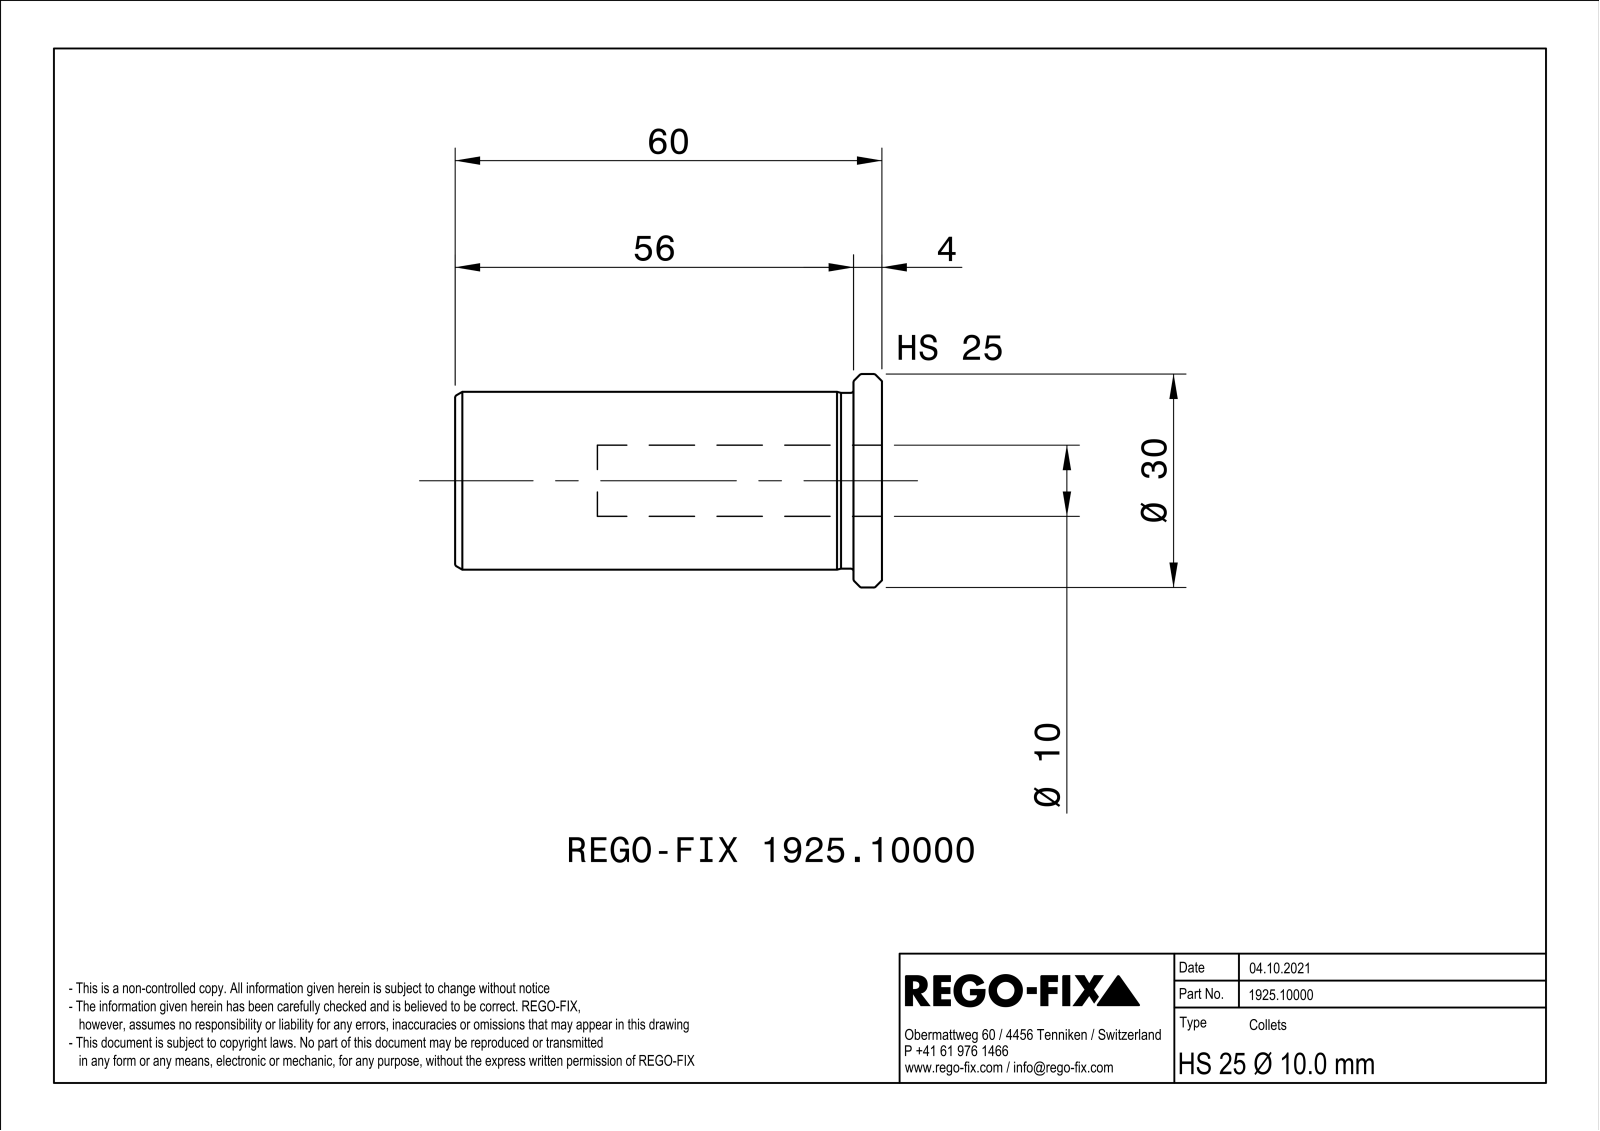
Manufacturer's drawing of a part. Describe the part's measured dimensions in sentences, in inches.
The part is named "NOCUT". Its 3-D file was written by "SIEMENS PLM Software Solid Edge ST10 (AUTOMOTIVE_DESIGN)". It is 1 solid with 174 faces: 96 planar, 12 cylindrical and 66 other. Overall it measures 2.362 by 1.18 by 1.18 inches. Its volume is 1.286 cubic inches and its surface area 15.94 square inches. Round holes: 1 of diameter 0.394, 1 of diameter 0.807. Round bosses or shafts: 1 of diameter 1.181, 1 of diameter 0.984, 1 of diameter 0.972. Partial cylindrical surfaces (rounded edges, fillets, slot ends): 1 of radius 14.903. The main face-to-face distances are 0.039, 0.157, 2.362, 2.205, 0.157, 2.362, 0.05, 0.06, 0.073, 0.05.
